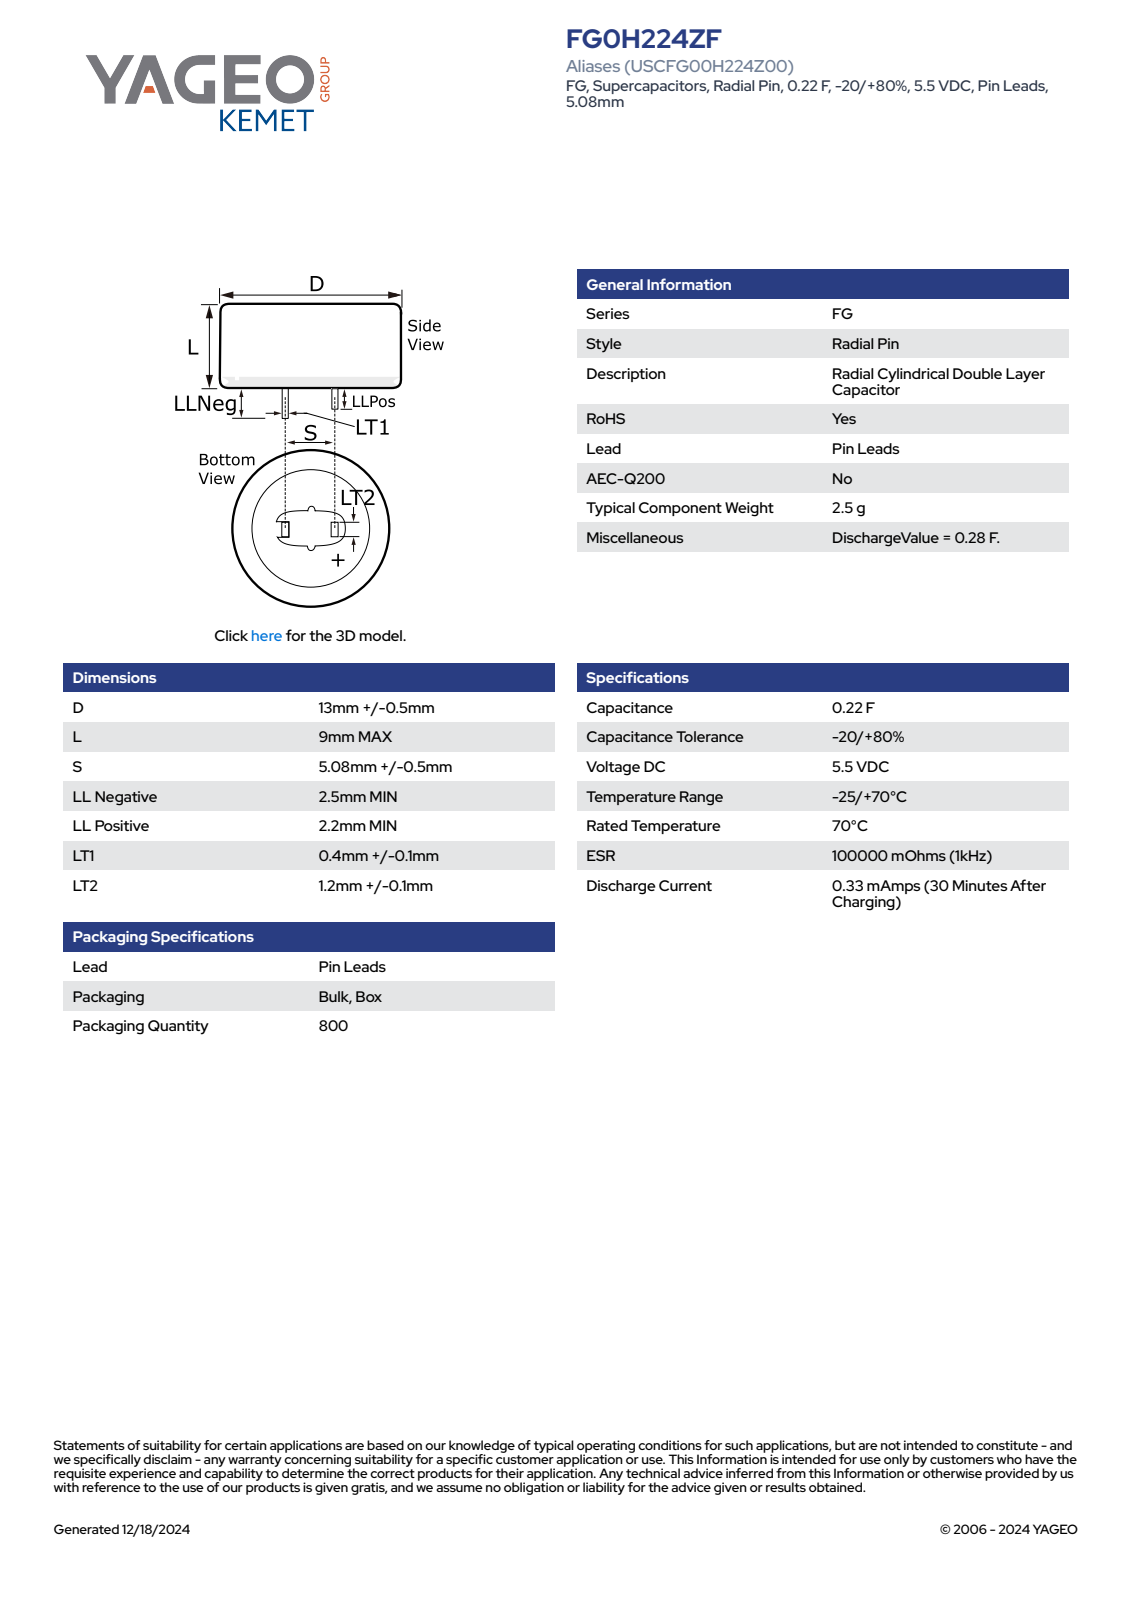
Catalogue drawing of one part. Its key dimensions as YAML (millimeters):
part_name: "CDR_LPLLN_D13.5L9S5.08LLNEG2.5LLPOS2.2LT10.5LT21.3"
step_written_by: "SolidWorks 2014 (AUTOMOTIVE_DESIGN)"
units: millimeters
bodies: {solids: 1, faces: 78, planar: 70, cylindrical: 4, other: 4}
overall_size: [13.5, 13.5, 11.5]
volume: 1285
surface_area: 664
round_bosses_or_shafts:
  - {diameter: 13.5, count: 1}
partial_cylinders:
  - {radius: 6.76, count: 1}
face_to_face_distances: [9, 8.99, 0.5, 5.08, 5.58, 4.58, 1.3, 2.2, 11.19, 11.2]
